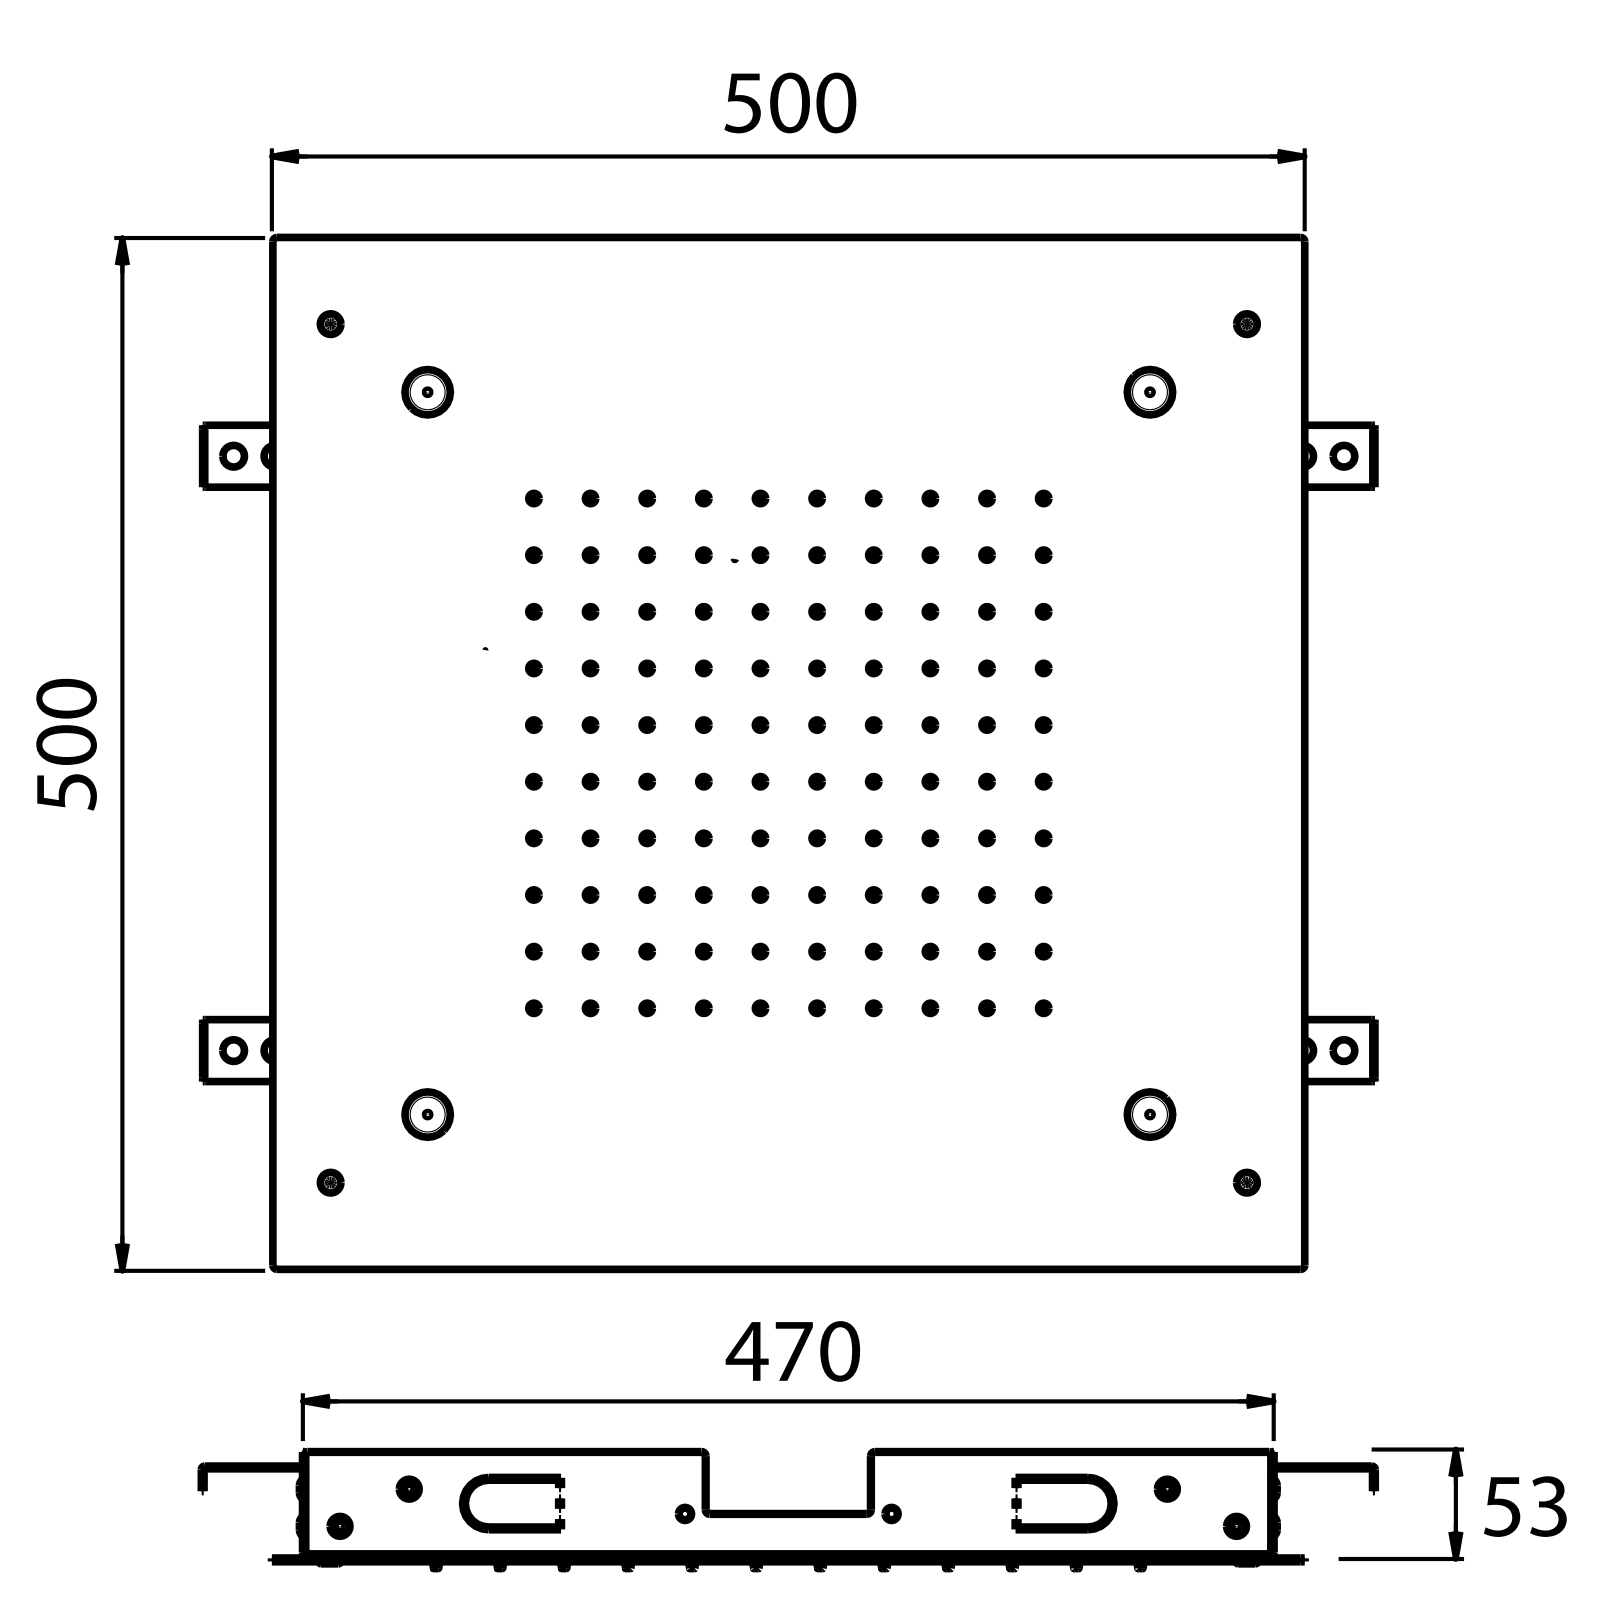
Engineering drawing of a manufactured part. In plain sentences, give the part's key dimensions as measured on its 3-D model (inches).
The part is named "A.R._24568/20220905". Its 3-D file was written by "Spatial InterOp 3D (AUTOMOTIVE_DESIGN)". It is 1 solid with 3593 faces: 1209 planar, 1106 cylindrical and 1278 other. Overall it measures 22.362 by 19.685 by 2.217 inches. Its volume is 53 cubic inches and its surface area 1 540 square inches. Round holes: 104 of diameter 0.059, 104 of diameter 0.197, 100 of diameter 0.067, 20 of diameter 0.244, 12 of diameter 0.205, 8 of diameter 0.102, 8 of diameter 0.236, 8 of diameter 0.402, 8 of diameter 0.413, 4 of diameter 0.165, 4 of diameter 0.173, 4 of diameter 0.177. Round bosses or shafts: 104 of diameter 0.394, 12 of diameter 0.236, 8 of diameter 0.386, 8 of diameter 0.323, 8 of diameter 0.272, 8 of diameter 0.189, 4 of diameter 0.866, 4 of diameter 0.787. Partial cylindrical surfaces (rounded edges, fillets, slot ends): 166 of radius 0.008, 96 of radius 0.079, 44 of radius 0.02, 32 of radius 0.039, 16 of radius 0.059, 12 of radius 0.004, 8 of radius 0.032, 8 of radius 0.046. The main face-to-face distances are 0.098, 0.039, 0.157, 0.059, 0.118, 0.217, 0.256, 0.02, 18.465, 0.138. The hole center spacings are 1.083, 2.421, 1.531, 2.165, 3.424, 3.248, 4.464, 6.586.
